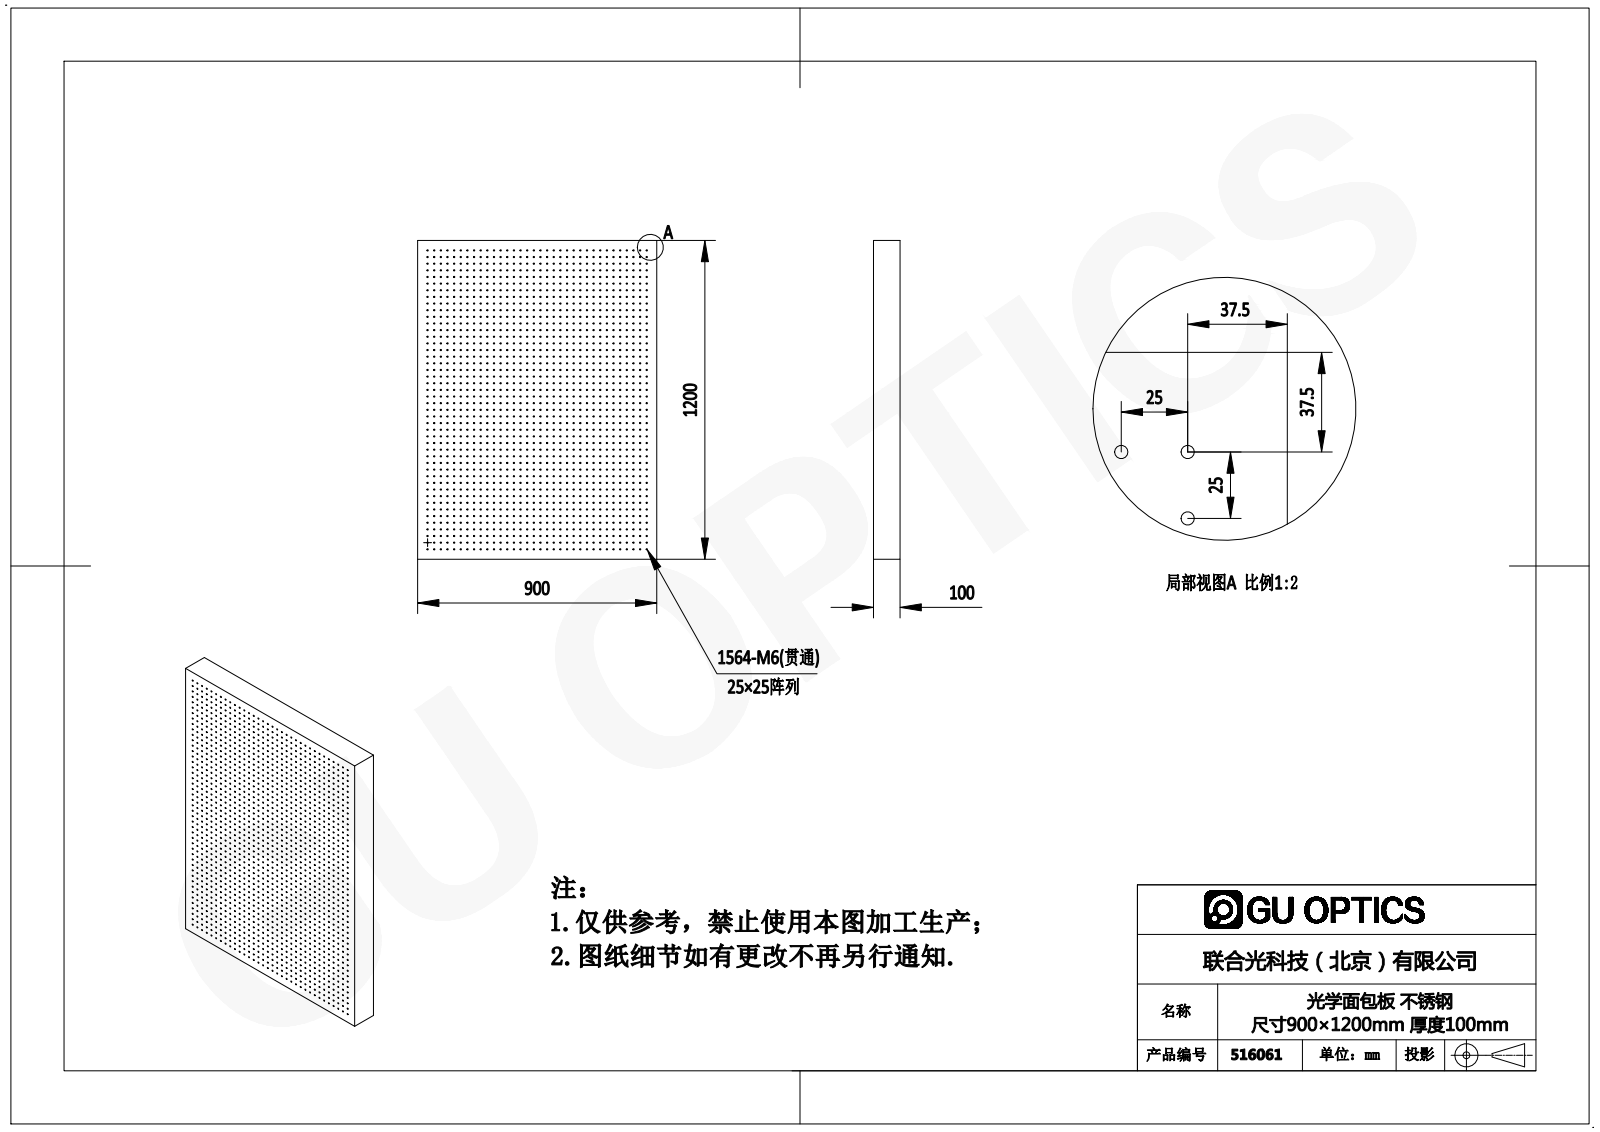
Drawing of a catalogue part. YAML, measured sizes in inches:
part_name: "516061"
step_written_by: "SolidWorks 2016 (AUTOMOTIVE_DESIGN)"
units: inches
bodies: {solids: 1, faces: 3134, planar: 6, cylindrical: 3128, other: 0}
overall_size: [47.244, 35.433, 3.937]
volume: 6401
surface_area: 7711
round_holes:
  - {diameter: 0.197, count: 1564}
face_to_face_distances: [3.937, 35.433, 47.244]
hole_center_spacings: [0.984, 1.969, 2.953, 3.937, 4.921, 5.906, 6.89, 7.874]
